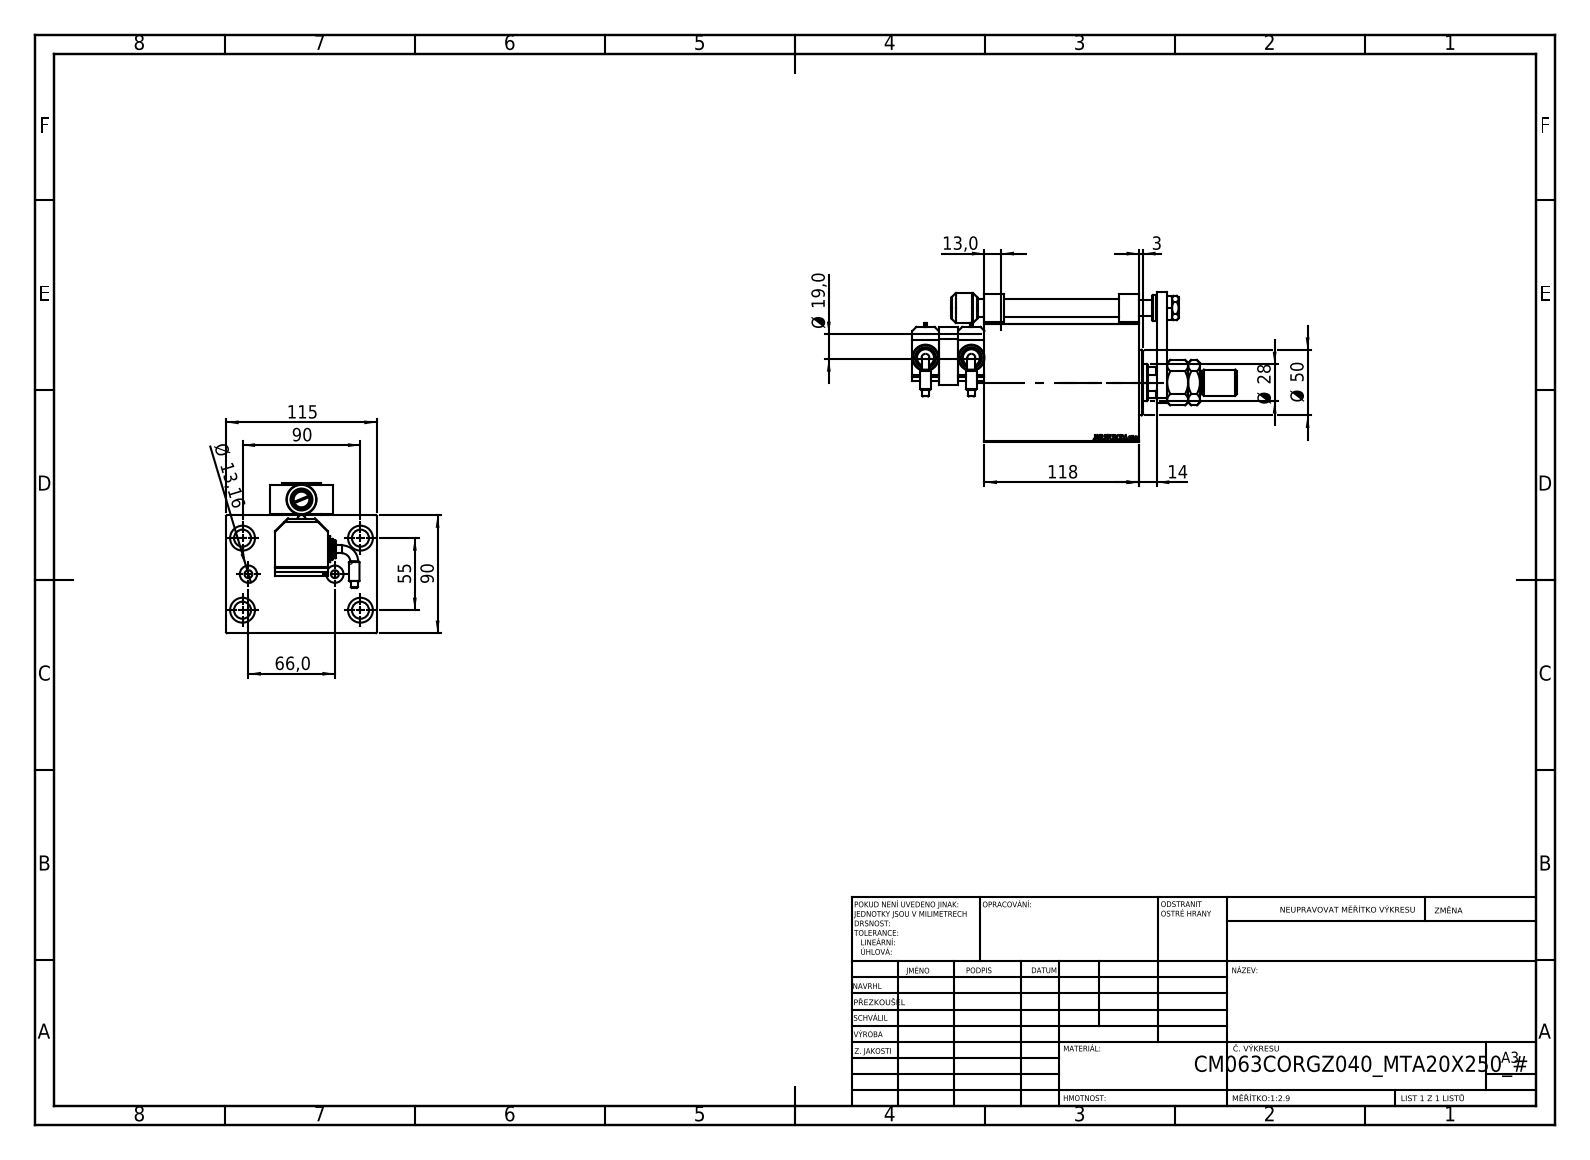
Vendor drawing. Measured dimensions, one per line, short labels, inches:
name: V450CM_C_Body; SWITCH P; KROUZEK_PRO_TYC; P_V_Z_MTA (+7 more)
written by: SolidWorks 2019 (CONFIG_CONTROL_DESIGN)
unit: in
bodies: 15 solids, 1162 faces (539 planar, 128 cylindrical, 495 other)
size: 9.744 × 4.528 × 4.508
volume: 75.36 in³; area: 313.4 in²
holes: 5× ⌀0.512, 4× ⌀0.157, 4× ⌀0.315, 4× ⌀0.748, 2× ⌀0.236, 2× ⌀0.518, 1× ⌀0.472, 1× ⌀0.551, 1× ⌀0.65, 1× ⌀0.728, 1× ⌀1.102, 1× ⌀1.24
bosses: 4× ⌀0.787, 2× ⌀0.63, 2× ⌀0.551, 2× ⌀0.315, 2× ⌀0.236, 2× ⌀0.198, 1× ⌀1.969, 1× ⌀0.906
rounds: 1× R0.118, 1× R0.531
face distances: 3.543, 4.528, 1.378, 4.646, 0.689, 3.957, 5.492, 1.476, 0.531, 0.591
hole spacings: 2.076, 0.787, 1.097, 1.327, 2.119, 2.165, 2.979, 3.536
